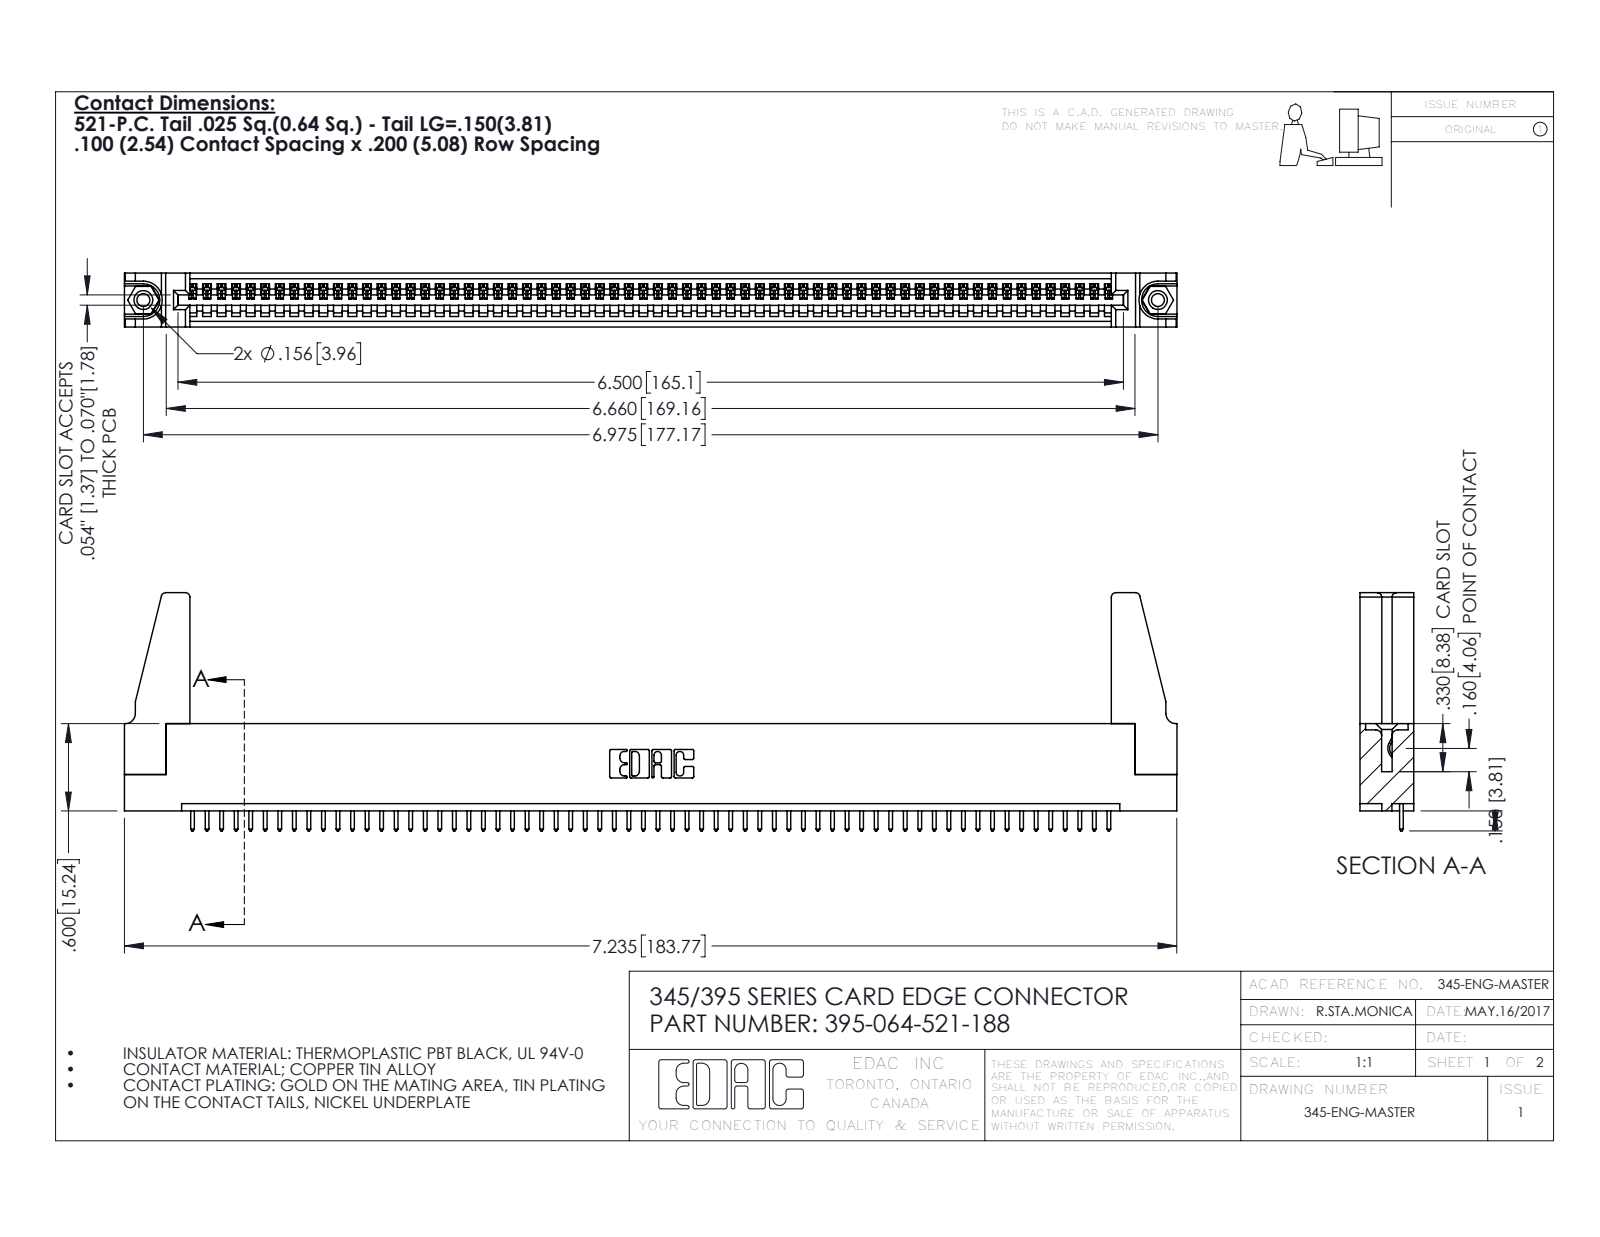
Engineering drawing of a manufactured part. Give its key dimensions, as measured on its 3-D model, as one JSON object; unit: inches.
{"part_name": "345-292-001_345-293-121; 345-220-078_345-220-088; 395-064-521-188; 345 Part_Flush Mounting Lugs - 0.156 Dia-TH (+1 more)", "step_written_by": "SolidWorks 2016 (CONFIG_CONTROL_DESIGN)", "units": "inches", "bodies": {"solids": 69, "faces": 3962, "planar": 2712, "cylindrical": 1234, "other": 16}, "overall_size": [7.236, 1.637, 0.37], "volume_in3": 1.264, "surface_area_in2": 40.16, "round_holes": [[0.089, 2], [0.125, 2], [0.156, 2], [0.064, 1]], "round_bosses_or_shafts": [[0.155, 2]], "partial_cylinders_radius": [[0.006, 128], [0.01, 128], [0.01, 22], [0.03, 8], [0.007, 6], [0.031, 6], [0.026, 3], [0.031, 2]], "face_to_face_distances": [0.072, 0.298, 0.37, 0.2, 0.098, 0.272, 0.025, 0.225, 0.149, 0.072], "hole_center_spacings": [0.27, 6.739, 6.975]}
